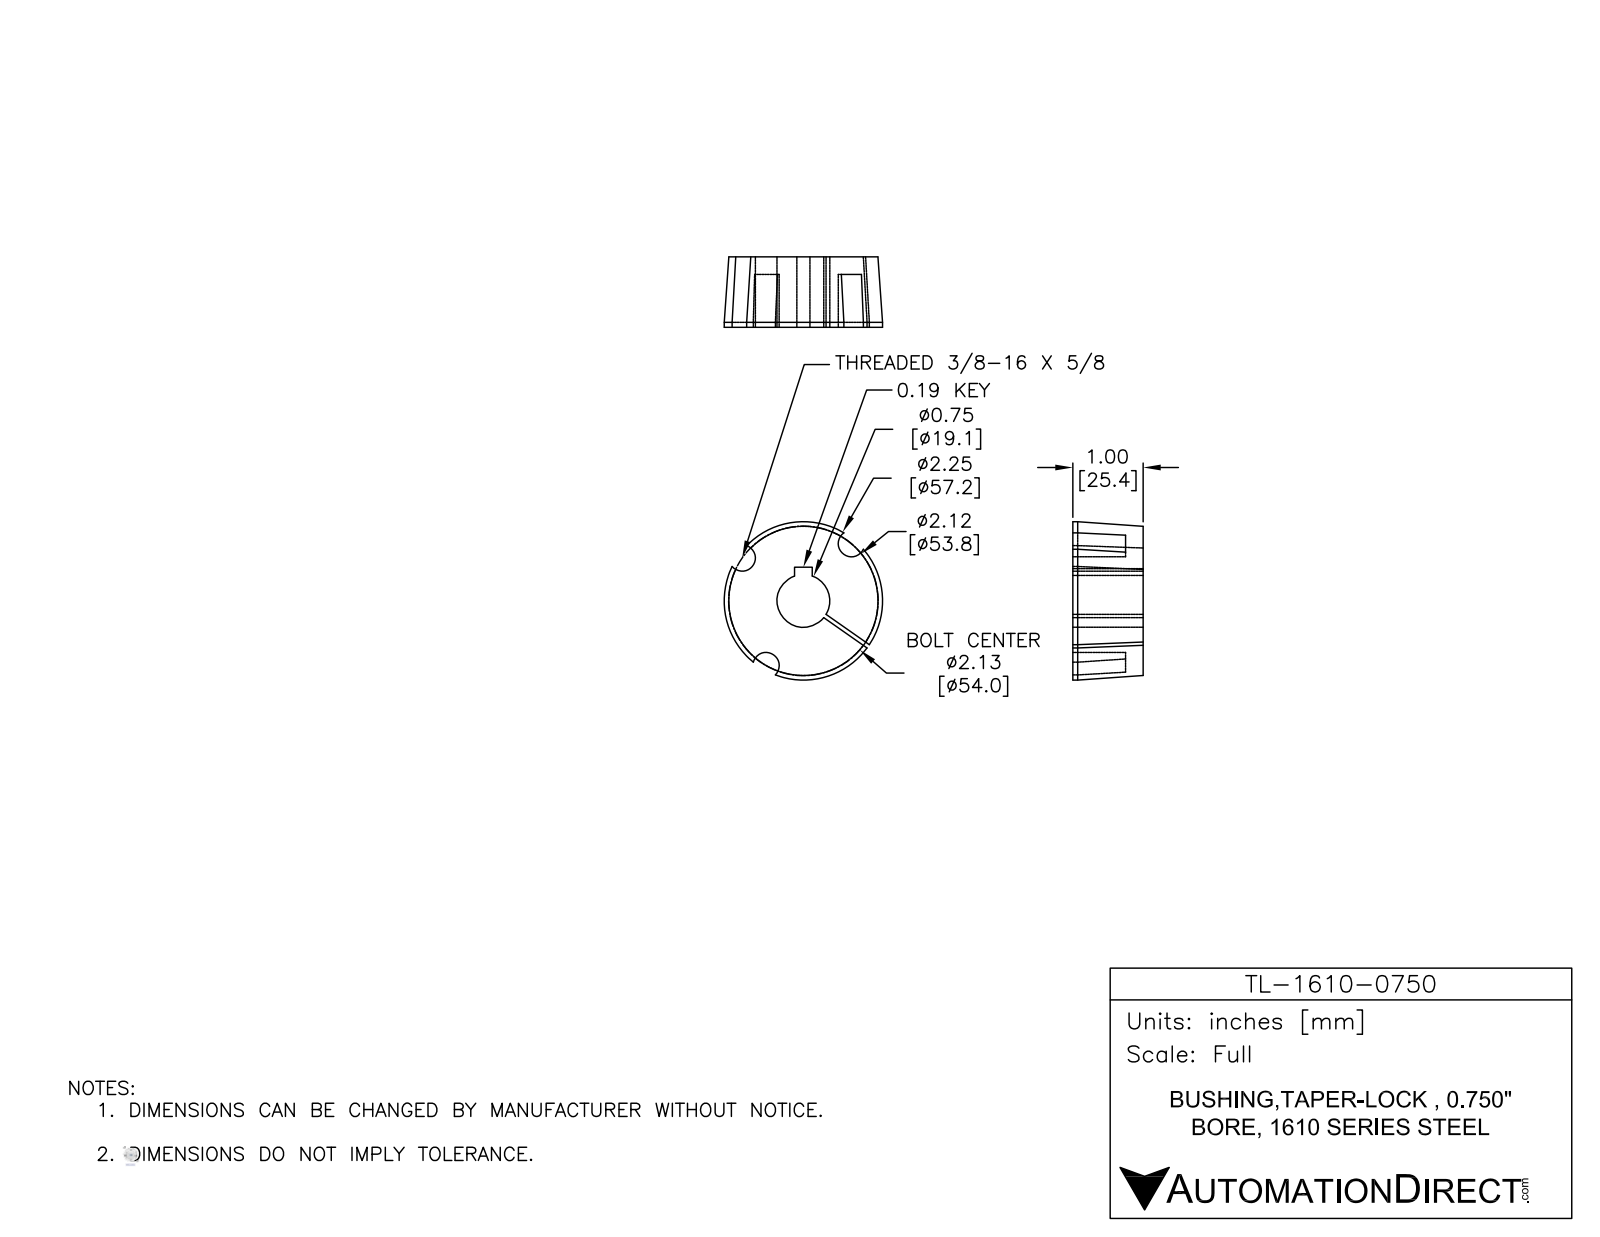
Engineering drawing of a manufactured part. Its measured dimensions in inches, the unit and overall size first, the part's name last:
Units: inches
Overall size (bounding box): 2.25 × 2.25 × 1
Round holes (diameter × count): ⌀0.75 ×1
Round bosses / shafts (diameter × count): ⌀2.25 ×1
Partial cylindrical surfaces — rounded edges, fillets, slot ends (radius × count): R0.188 ×3
Main face-to-face distances: 1, 0.057, 0.25, 0.75, 0.187
Volume: 3.101 in³ · Surface area: 17.75 in²
Bodies: 1 solid, 25 faces (9 planar, 13 cylindrical, 3 other)
Part name (STEP PRODUCT): TL-1610-0750
STEP written by: SolidWorks 2014 (AUTOMOTIVE_DESIGN)
